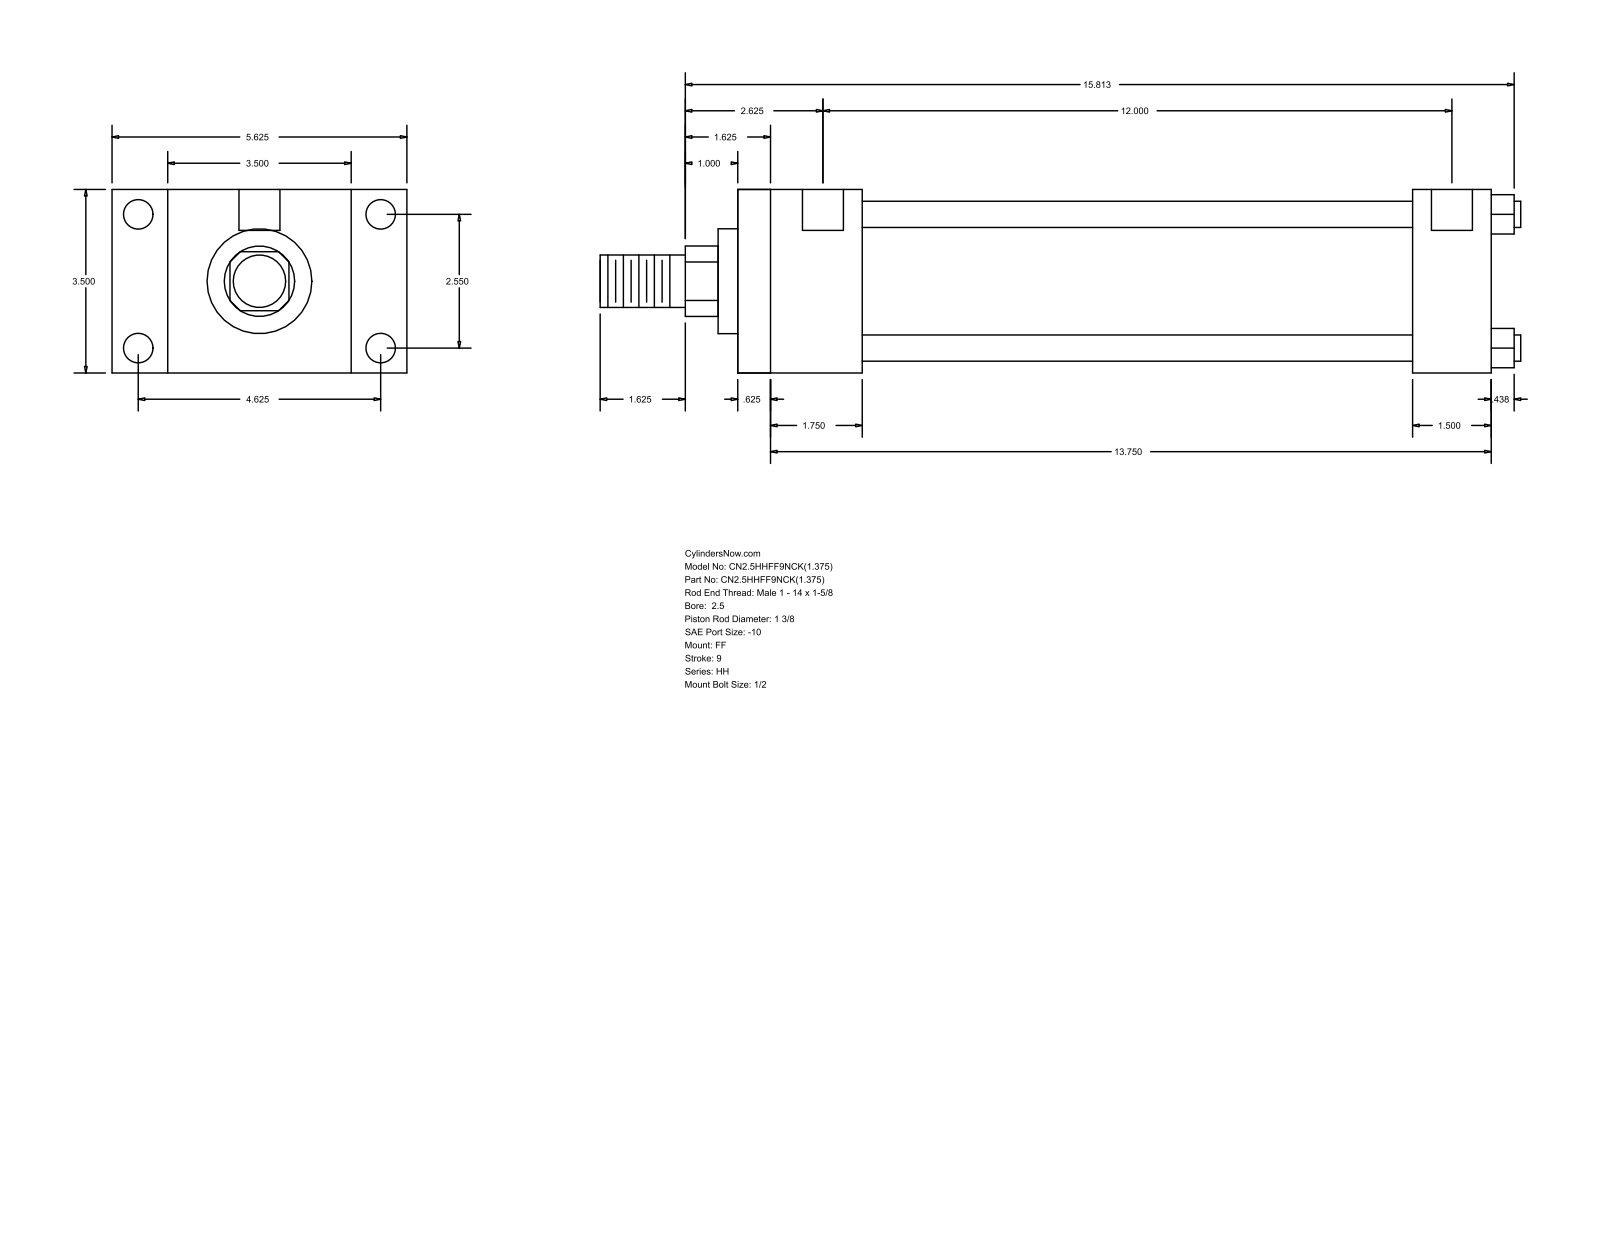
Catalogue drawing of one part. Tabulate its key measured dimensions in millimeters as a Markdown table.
| quantity | value |
| --- | --- |
| part name | HH_FF__0250_1.375 |
| STEP written by | GSSL Pune (CONFIG_CONTROL_DESIGN) |
| units | millimeters |
| bodies | 0 solids, 92 faces (64 planar, 28 cylindrical, 0 other) |
| overall size | 446.09 × 142.88 × 88.9 |
| round holes (diameter × count) | 5.56 × 4, 14.3 × 4, 19.84 × 2 |
| round bosses / shafts (diameter × count) | 12.7 × 4, 73.03 × 1, 50.8 × 1, 34.92 × 1, 25.4 × 1 |
| partial cylindrical surfaces (radius × count) | 17.06 × 1 |
| main face-to-face distances | 88.9, 365.12, 15.87, 349.25, 60.32, 44.45, 304.8, 327.03, 311.16, 266.71 |
| hole center spacings | 1.58, 64.76, 117.48, 134.15, 306.39, 307.97, 304.81 |
